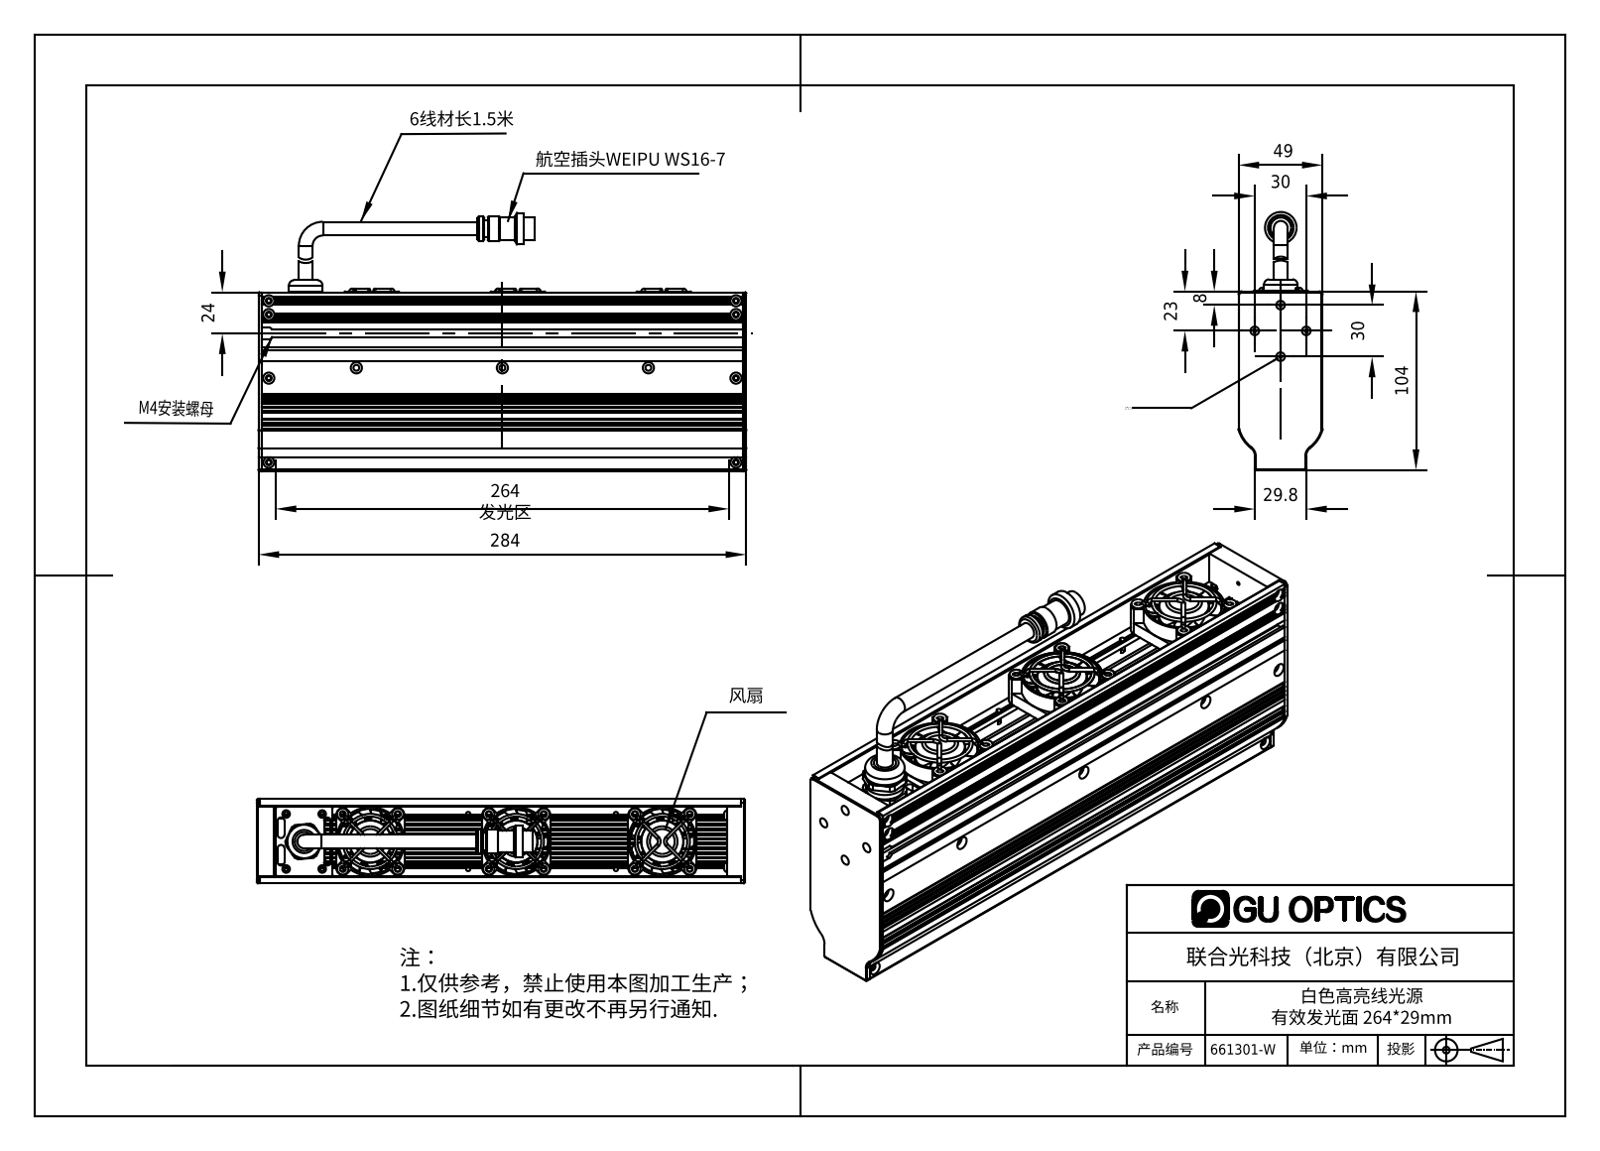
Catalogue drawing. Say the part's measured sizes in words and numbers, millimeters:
The part is named "661301-W". Its 3-D file was written by "SolidWorks 2016 (AUTOMOTIVE_DESIGN)". It is 31 solids with 2506 faces: 981 planar, 776 cylindrical and 749 other. Overall it measures 284 by 150.2 by 49 millimeters. Its volume is 800 872 cubic millimeters and its surface area 379 288 square millimeters. Round holes: 25 of diameter 2.5, 12 of diameter 3.2, 12 of diameter 6.2, 11 of diameter 3.4, 10 of diameter 1.6, 10 of diameter 3.5, 9 of diameter 6.5, 6 of diameter 1, 4 of diameter 2.4, 4 of diameter 5, 3 of diameter 38, 1 of diameter 11. Round bosses or shafts: 12 of diameter 1.6, 3 of diameter 24.8, 3 of diameter 24, 3 of diameter 2, 2 of diameter 8, 1 of diameter 35, 1 of diameter 19.5, 1 of diameter 19. Partial cylindrical surfaces (rounded edges, fillets, slot ends): 58 of radius 1, 28 of radius 0.2, 20 of radius 2, 13 of radius 5.1, 12 of radius 0.4, 10 of radius 0.5, 7 of radius 3, 6 of radius 1.11. The main face-to-face distances are 2, 5.5, 5, 11, 5.1, 43.9, 3.8, 1.7, 48.9, 43.8. The hole center spacings are 32, 3.5, 85, 86, 31.82, 45, 26.8, 3.51.
